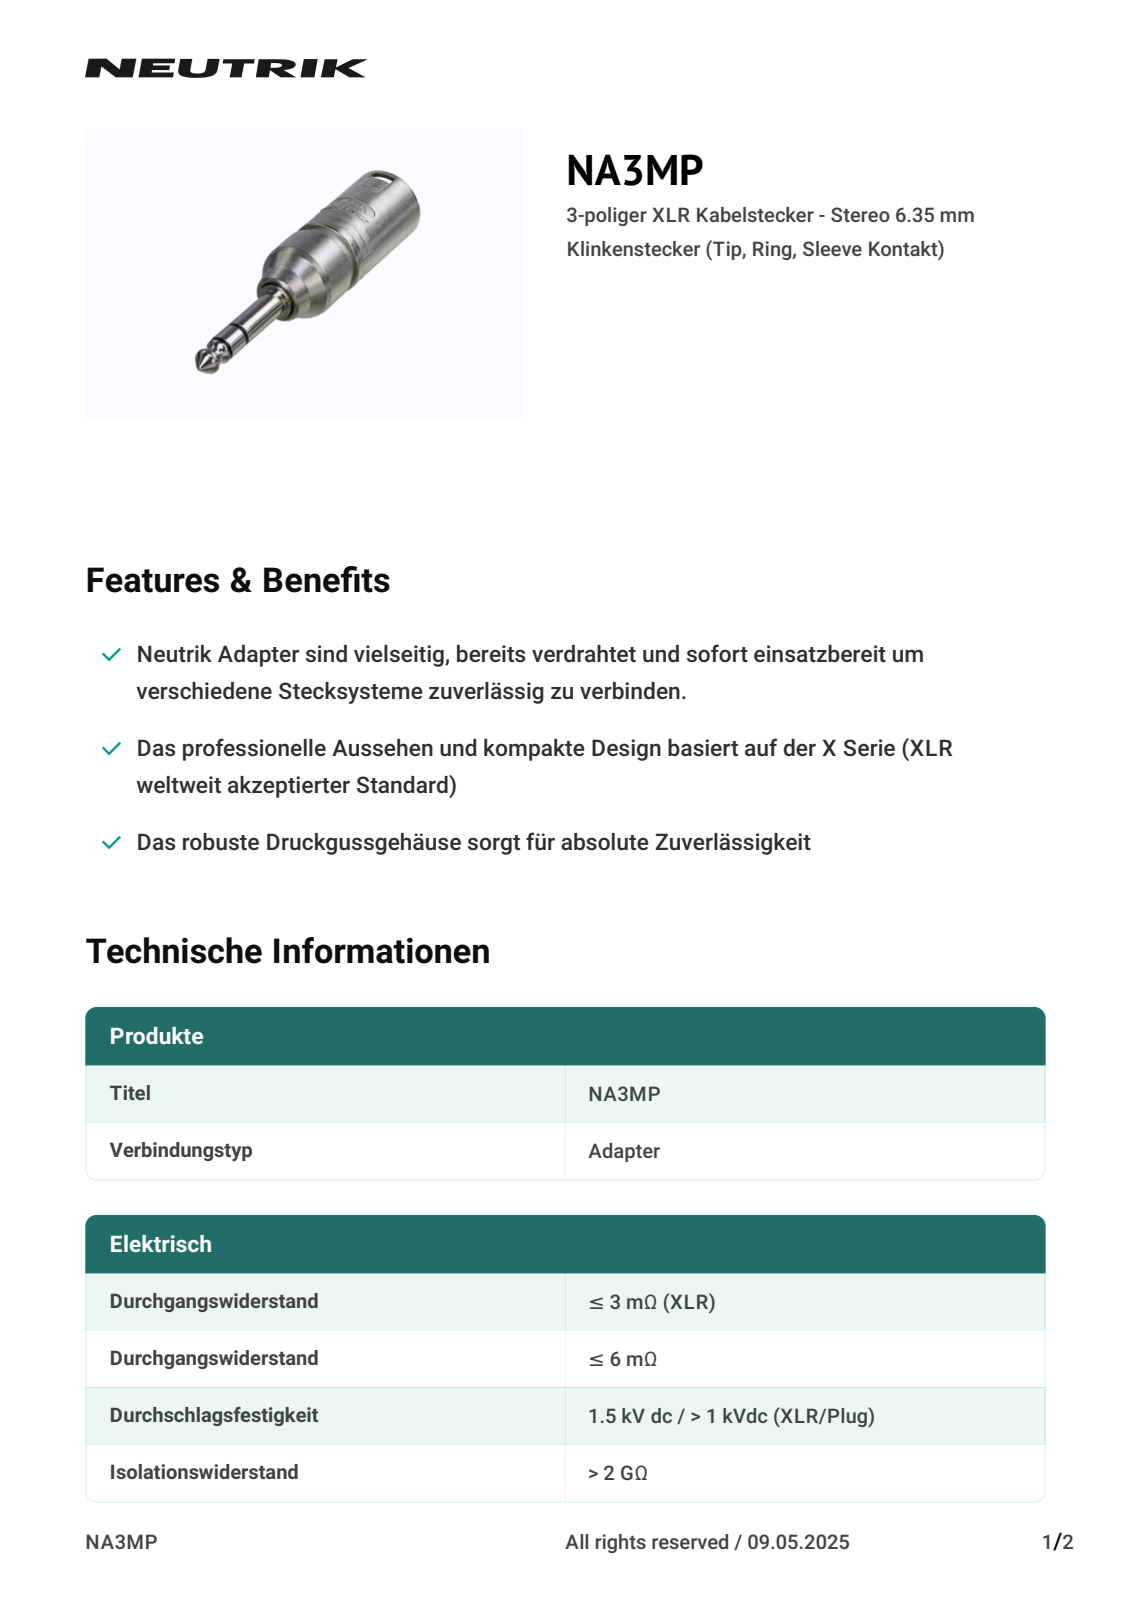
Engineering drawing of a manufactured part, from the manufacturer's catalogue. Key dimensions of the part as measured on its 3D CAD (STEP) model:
Part name (STEP PRODUCT): NA3MP
STEP written by: CREO PARAMETRIC BY PTC INC, 2018360 (CONFIG_CONTROL_DESIGN)
Units: millimetres
Bodies: 1 solid, 667 faces (521 planar, 84 cylindrical, 62 other)
Overall size (bounding box): 79.67 × 19.2 × 19
Volume: 10 645 mm³ · Surface area: 4 978 mm²
Round holes (diameter × count): ⌀2.41 ×3, ⌀5 ×1, ⌀9.1 ×1, ⌀13 ×1
Round bosses / shafts (diameter × count): ⌀2.38 ×3, ⌀19 ×1, ⌀12.9 ×1, ⌀8.95 ×1, ⌀6.29 ×1, ⌀6.15 ×1, ⌀6.1 ×1, ⌀5.3 ×1
Partial cylindrical surfaces — rounded edges, fillets, slot ends (radius × count): R0.25 ×9, R0.5 ×5, R0.21 ×1, R0.26 ×1, R0.52 ×1, R0.66 ×1, R1 ×1, R1.5 ×1
Main face-to-face distances: 15.6, 33.6, 1.1, 18, 2.5, 14.4, 30, 48, 49.1, 34.7
Hole centre spacings: 4.05, 5.66, 3.95, 8.1
